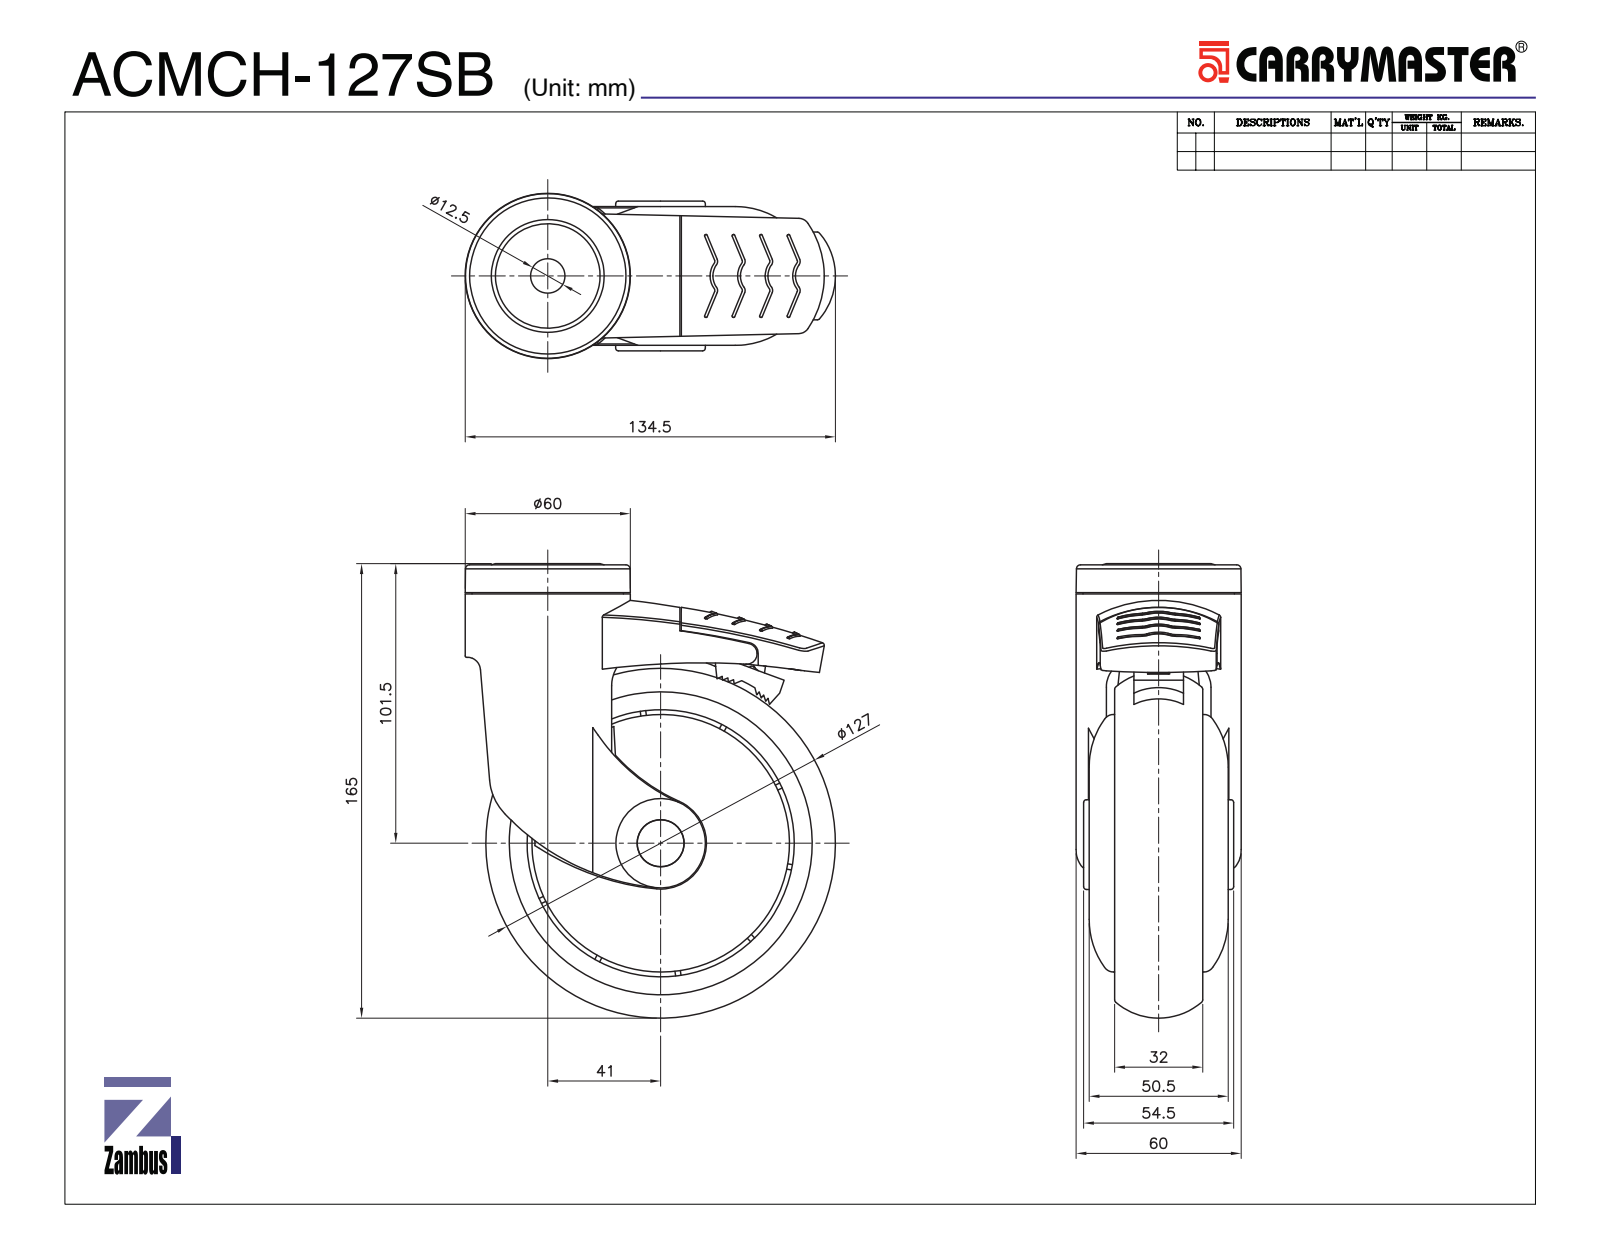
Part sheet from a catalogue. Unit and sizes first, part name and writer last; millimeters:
Units: millimetres
Overall size (bounding box): 165 × 134.5 × 60
Round holes (diameter × count): ⌀12.5 ×1, ⌀17 ×1, ⌀38 ×1, ⌀55 ×1, ⌀97 ×1, ⌀110.01 ×1
Round bosses / shafts (diameter × count): ⌀110 ×1, ⌀93.5 ×1, ⌀60 ×1, ⌀53 ×1, ⌀32.5 ×1, ⌀30 ×1, ⌀16.9 ×1
Partial cylindrical surfaces — rounded edges, fillets, slot ends (radius × count): R30 ×5, R0.5 ×4, R4 ×4, R1 ×3, R2 ×2, R7 ×2, R274.03 ×2, R1.07 ×1
Main face-to-face distances: 3, 35, 38, 8, 11, 32, 18, 6.25, 9.25, 41.25
Volume: 581 788 mm³ · Surface area: 107 902 mm²
Bodies: 4 solids, 535 faces (143 planar, 132 cylindrical, 260 other)
Part name (STEP PRODUCT): ACMCH-127SB; ACMCH-127 WHEEL; ACMCH-127SB BRAKE; ACMCH-127SB BRAKE 2 (+1 more)
STEP written by: SolidWorks 2019 (CONFIG_CONTROL_DESIGN)
